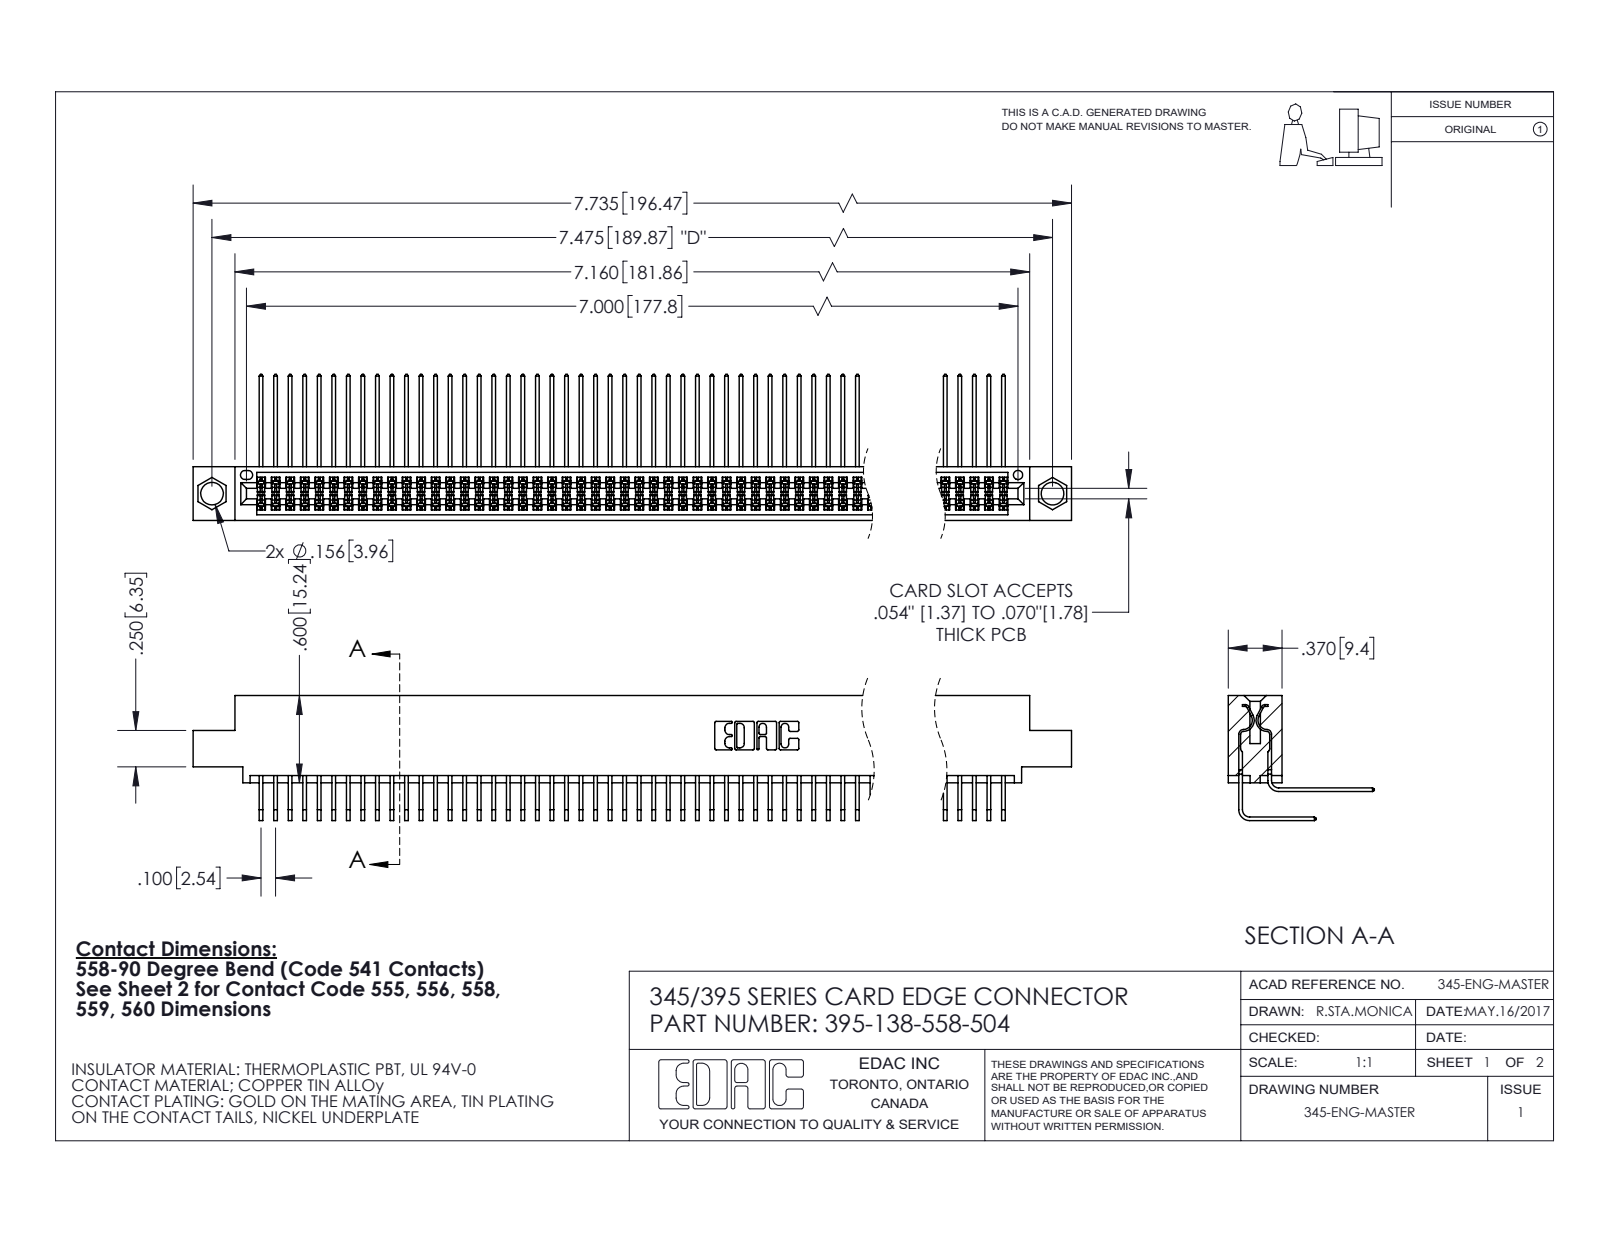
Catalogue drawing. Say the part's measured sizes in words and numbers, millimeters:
The part is named "345 Part_0.110 Offset - 0.156 Dia-TI; 345-292-001_558 Tail - 2; 395-138-558-504; 345-292-001_558 559 Tail - 1". Its 3-D file was written by "SolidWorks 2020 (CONFIG_CONTROL_DESIGN)". It is 139 solids with 7320 faces: 4928 planar, 2392 cylindrical and 0 other. Overall it measures 196.5 by 25.5 by 21.8 millimeters. Its volume is 19 960 cubic millimeters and its surface area 33 700 square millimeters. Round holes: 2 of diameter 4, 1 of diameter 1.6. Partial cylindrical surfaces (rounded edges, fillets, slot ends): 275 of radius 0.2, 22 of radius 0.3, 6 of radius 0.2, 6 of radius 0.8, 3 of radius 0.7, 2 of radius 0.4, 2 of radius 0.5, 2 of radius 0.6. The main face-to-face distances are 1.8, 7.6, 5.1, 9.4, 2.5, 6.9, 0.6, 5.7, 0.6, 4.4. The hole center spacings are 6.9, 183.9, 189.9.
